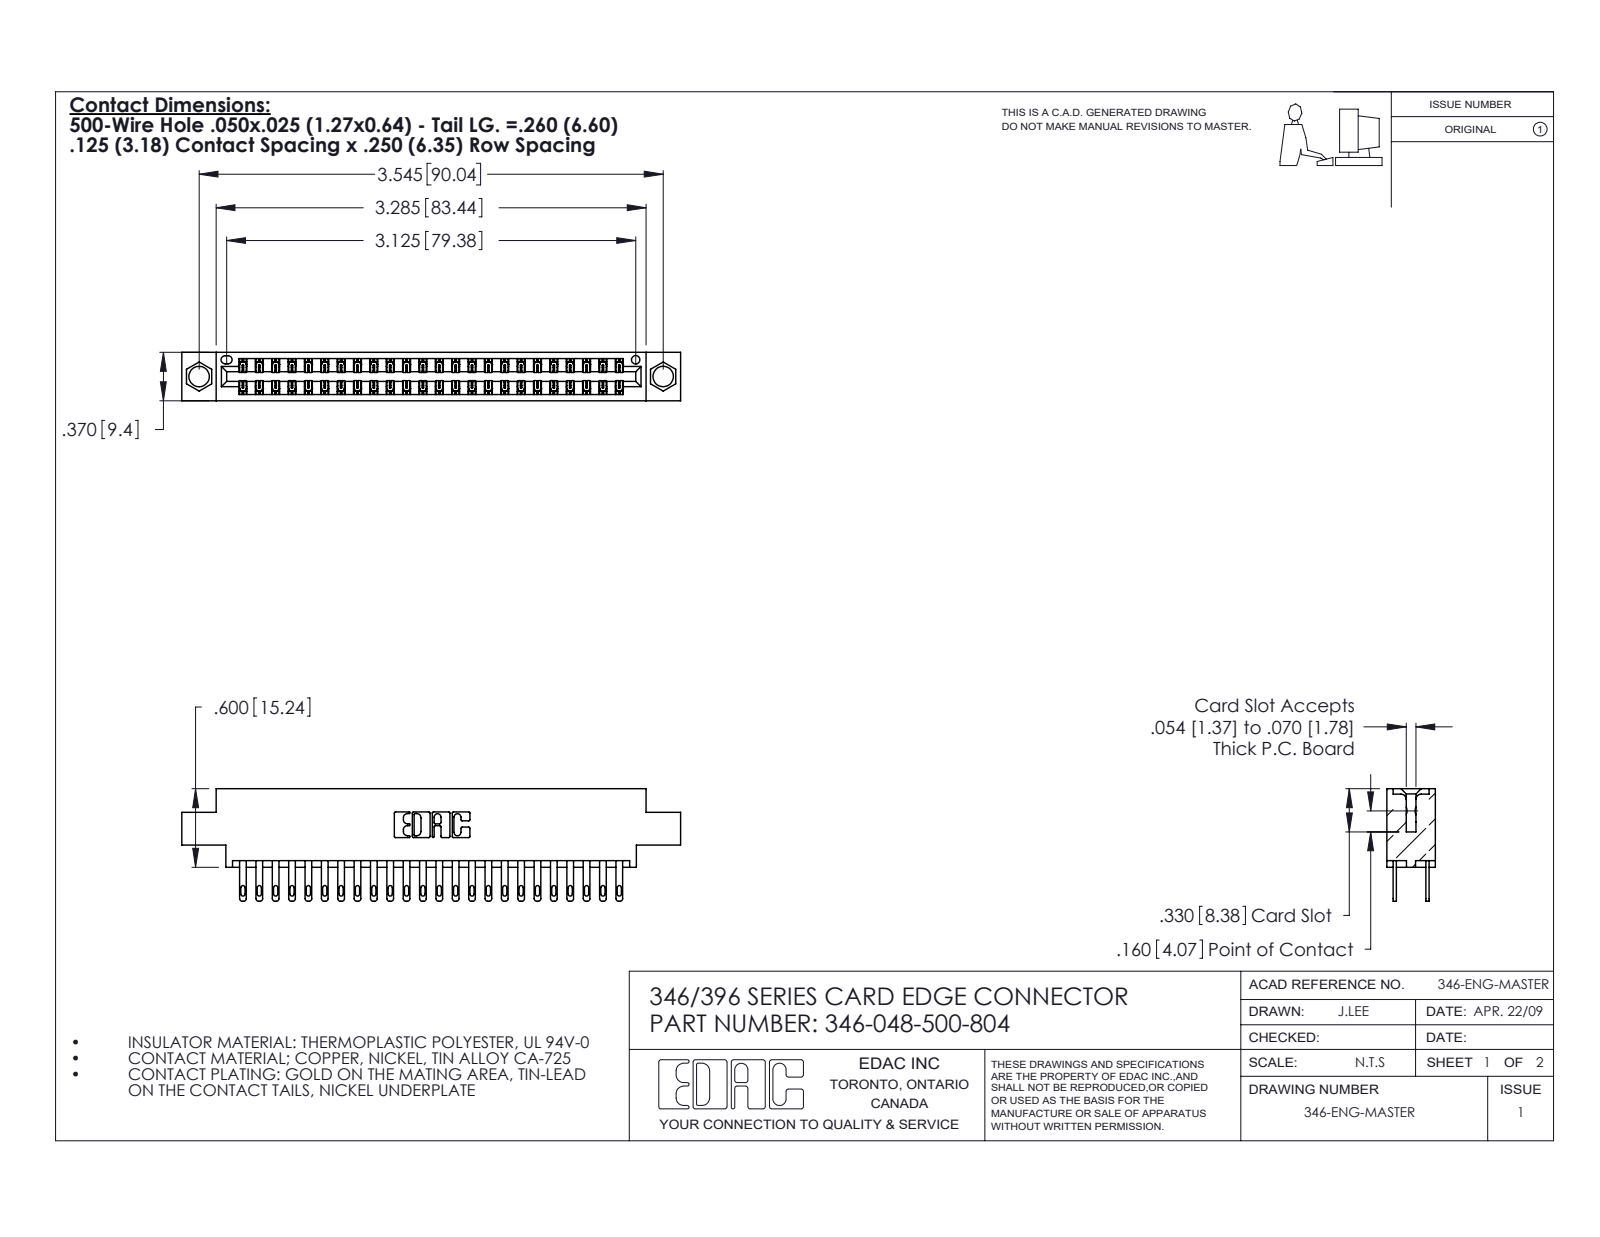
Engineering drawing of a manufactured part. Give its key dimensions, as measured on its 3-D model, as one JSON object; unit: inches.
{"part_name": "346-048-500-804; 346 Part_0.170 Offset - 0.156 Dia-TH; 345-292-001_345-293-100", "step_written_by": "SolidWorks 2020 (CONFIG_CONTROL_DESIGN)", "units": "inches", "bodies": {"solids": 49, "faces": 2444, "planar": 1486, "cylindrical": 958, "other": 0}, "overall_size": [3.81, 0.86, 0.37], "volume_in3": 0.56, "surface_area_in2": 19.95, "round_holes": [[0.156, 2], [0.064, 1]], "partial_cylinders_radius": [[0.006, 72], [0.016, 48], [0.02, 48], [0.01, 22], [0.007, 6], [0.031, 6], [0.026, 3], [0.014, 2]], "face_to_face_distances": [0.048, 0.322, 0.25, 0.37, 0.072, 0.298, 0.025, 0.275, 0.222, 0.148], "hole_center_spacings": [0.246, 3.337, 3.545]}
